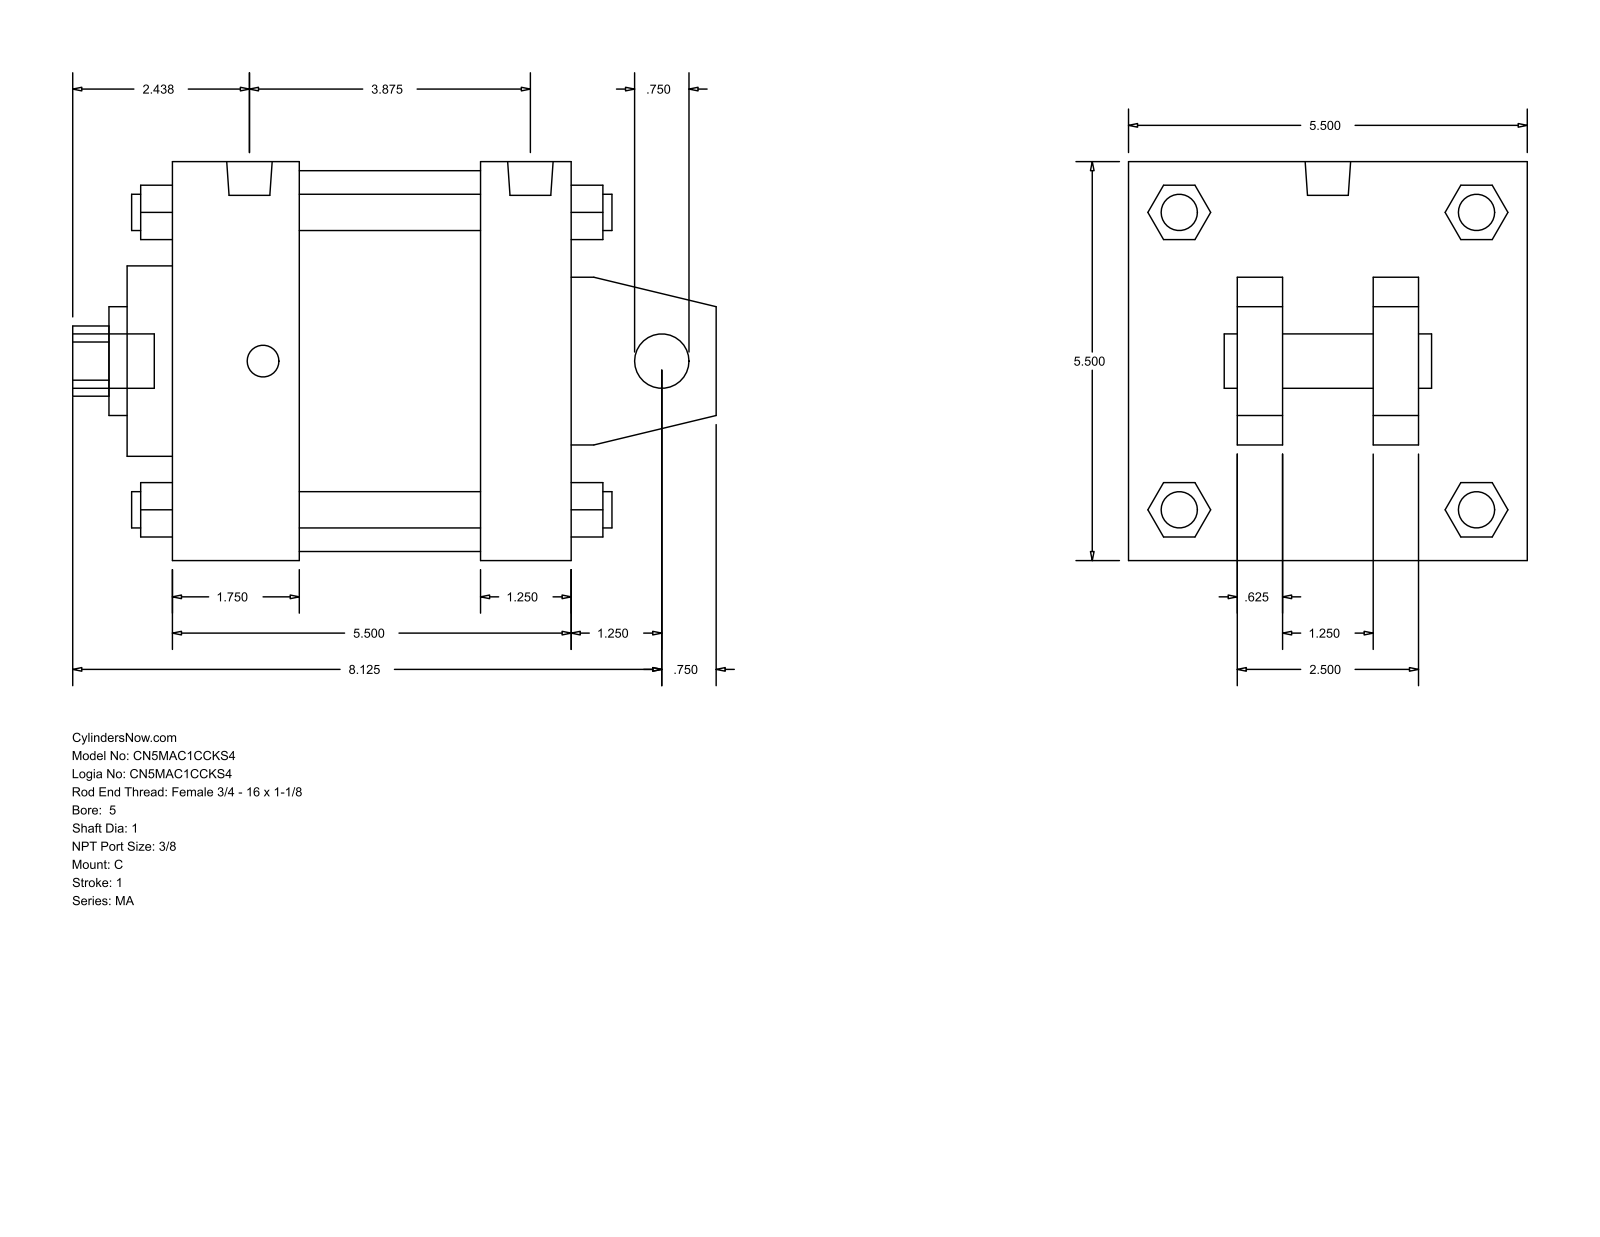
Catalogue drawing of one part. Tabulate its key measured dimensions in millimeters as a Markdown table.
| quantity | value |
| --- | --- |
| part name | MA_C__0500_1 |
| STEP written by | GSSL Pune (CONFIG_CONTROL_DESIGN) |
| units | millimeters |
| bodies | 0 solids, 141 faces (109 planar, 32 cylindrical, 0 other) |
| overall size | 225.43 × 139.7 × 139.7 |
| round holes (diameter × count) | 19.05 × 1, 25.4 × 1, 38.1 × 1, 66.67 × 1, 133.35 × 1 |
| round bosses / shafts (diameter × count) | 12.7 × 4, 11.11 × 4, 15.93 × 2, 19.05 × 1 |
| partial cylindrical surfaces (radius × count) | 12.29 × 1 |
| main face-to-face distances | 139.7, 63.5, 15.87, 107.96, 31.74, 44.46, 95.24, 38.1, 101.6, 53.97 |
